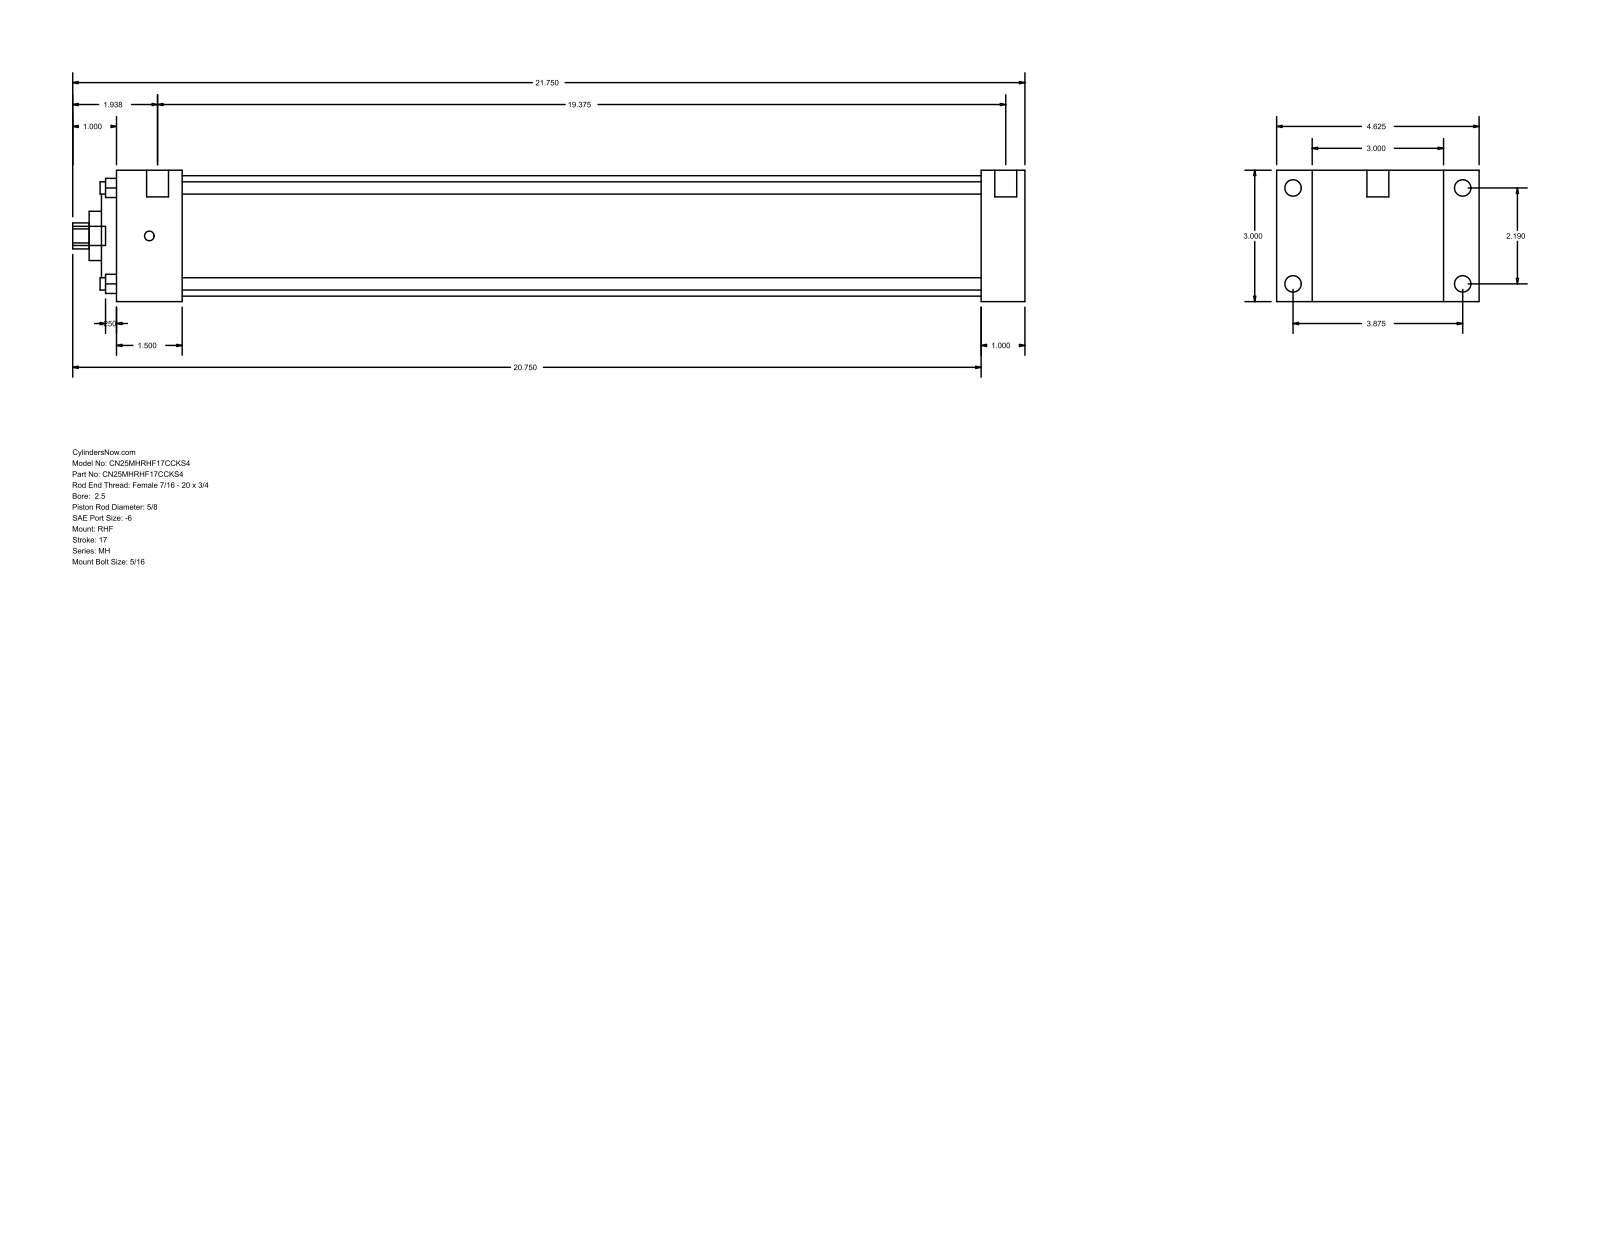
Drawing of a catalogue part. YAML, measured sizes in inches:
part_name: "MH_RHF__0250_0.625"
step_written_by: "GSSL Pune (CONFIG_CONTROL_DESIGN)"
units: inches
bodies: {solids: 0, faces: 90, planar: 61, cylindrical: 29, other: 0}
overall_size: [21.75, 4.625, 3]
round_holes:
  - {diameter: 0.281, count: 4}
  - {diameter: 0.625, count: 1}
  - {diameter: 1.125, count: 1}
  - {diameter: 2.187, count: 1}
  - {diameter: 2.75, count: 1}
round_bosses_or_shafts:
  - {diameter: 0.375, count: 4}
  - {diameter: 0.219, count: 4}
  - {diameter: 0.5, count: 2}
  - {diameter: 0.437, count: 1}
partial_cylinders:
  - {radius: 0.297, count: 1}
face_to_face_distances: [3, 1, 0.813, 3.813, 20.75, 19.75, 4.625, 1.5, 18.25, 19.25]
hole_center_spacings: [1.548, 2.19, 3.097]
